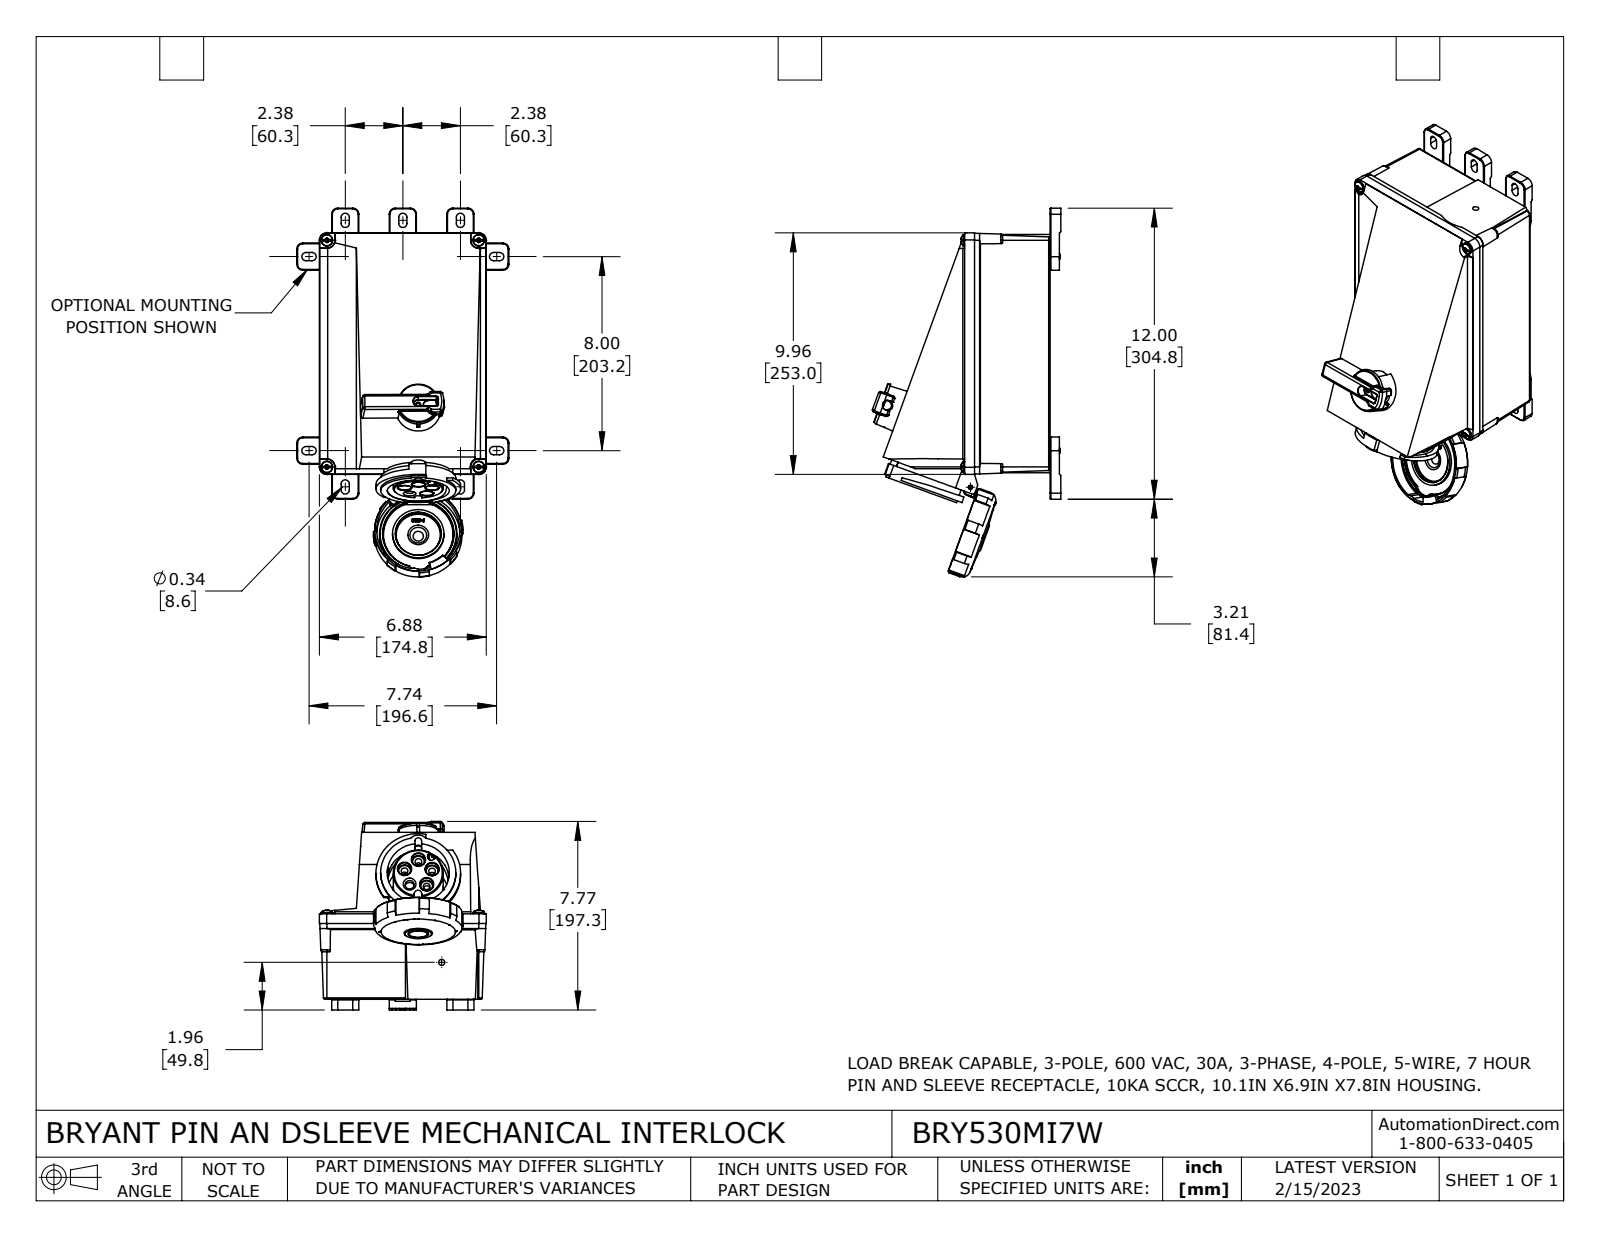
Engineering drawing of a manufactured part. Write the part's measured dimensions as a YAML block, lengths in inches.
part_name: "BRY530MI7W"
step_written_by: "SolidWorks 2021 (CONFIG_CONTROL_DESIGN)"
units: inches
bodies: {solids: 14, faces: 2494, planar: 869, cylindrical: 714, other: 911}
overall_size: [15.213, 7.77, 6.88]
volume: 324.4
surface_area: 687
round_holes:
  - {diameter: 0.094, count: 6}
  - {diameter: 0.281, count: 5}
  - {diameter: 0.078, count: 4}
  - {diameter: 0.28, count: 4}
  - {diameter: 0.15, count: 3}
  - {diameter: 0.157, count: 2}
  - {diameter: 0.101, count: 1}
  - {diameter: 0.159, count: 1}
  - {diameter: 0.19, count: 1}
  - {diameter: 0.27, count: 1}
  - {diameter: 0.67, count: 1}
  - {diameter: 0.775, count: 1}
round_bosses_or_shafts:
  - {diameter: 0.473, count: 9}
  - {diameter: 0.263, count: 2}
  - {diameter: 0.121, count: 2}
  - {diameter: 3.19, count: 1}
  - {diameter: 3.1, count: 1}
  - {diameter: 2.839, count: 1}
  - {diameter: 2.117, count: 1}
  - {diameter: 2.083, count: 1}
partial_cylinders:
  - {radius: 0.015, count: 135}
  - {radius: 0.03, count: 58}
  - {radius: 0.08, count: 30}
  - {radius: 0.09, count: 24}
  - {radius: 0.02, count: 22}
  - {radius: 0.075, count: 12}
  - {radius: 0.17, count: 10}
  - {radius: 0.25, count: 10}
face_to_face_distances: [3.12, 9.83, 0.12, 0.035, 0.38, 0.14, 4.847, 0.14, 0.041, 4.812]
hole_center_spacings: [0.7, 0.58, 3.761, 0.829, 8, 0.519, 0.56, 0.904]
